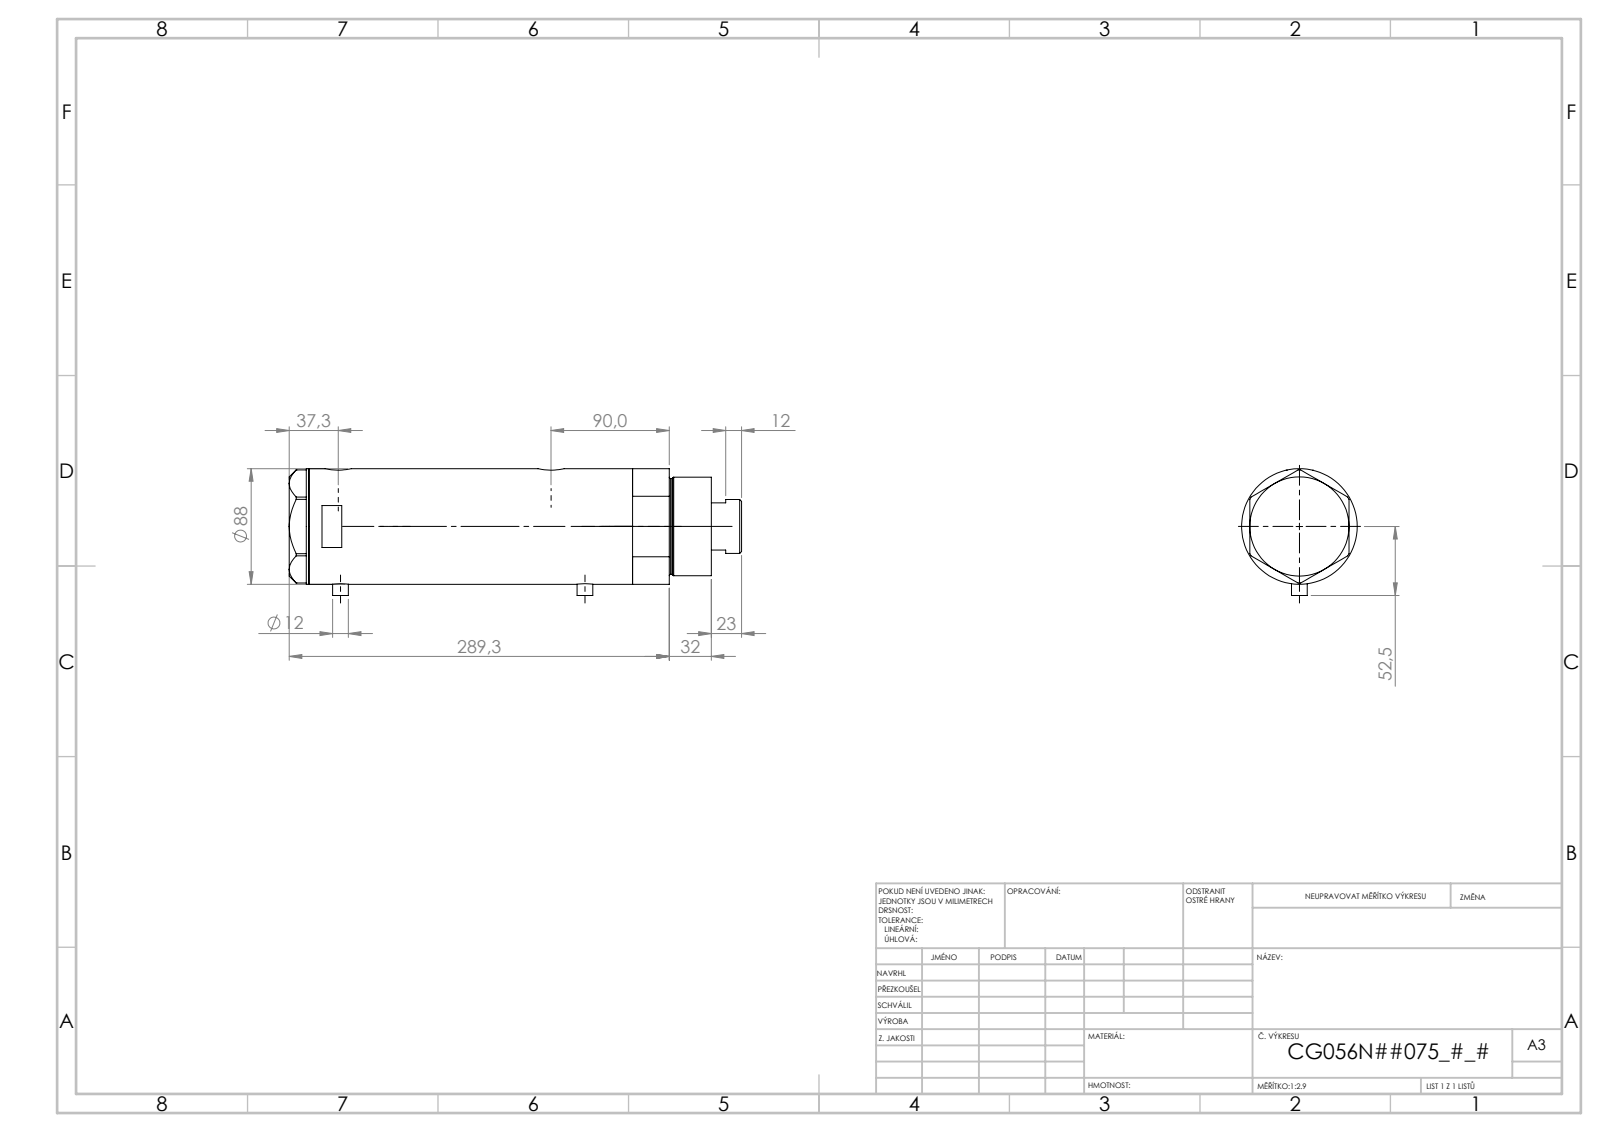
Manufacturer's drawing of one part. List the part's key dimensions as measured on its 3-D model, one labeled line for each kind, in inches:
Part name (STEP PRODUCT): V270CG_BACK; V270CG_FRONT; V270CG_VC; V270CG_MIDDLE
STEP written by: SolidWorks 2019 (CONFIG_CONTROL_DESIGN)
Units: inches
Bodies: 4 solids, 126 faces (53 planar, 53 cylindrical, 20 other)
Overall size (bounding box): 11.79 × 3.508 × 3.465
Volume: 93.79 in³ · Surface area: 347.3 in²
Round holes (diameter × count): ⌀0.197 ×2, ⌀0.492 ×2, ⌀0.518 ×2, ⌀0.787 ×2, ⌀0.571 ×1, ⌀1.654 ×1, ⌀1.713 ×1, ⌀2.205 ×1, ⌀2.362 ×1, ⌀3.15 ×1
Round bosses / shafts (diameter × count): ⌀0.472 ×2, ⌀3.465 ×1, ⌀2.953 ×1, ⌀2.874 ×1, ⌀1.614 ×1
Main face-to-face distances: 5.882, 1.024, 4.858, 0.591, 1.614, 6.472, 10.294, 10.885, 9.27, 4.412
Hole centre spacings: 0.067, 1.016, 4.933, 5, 5.949, 6.016
